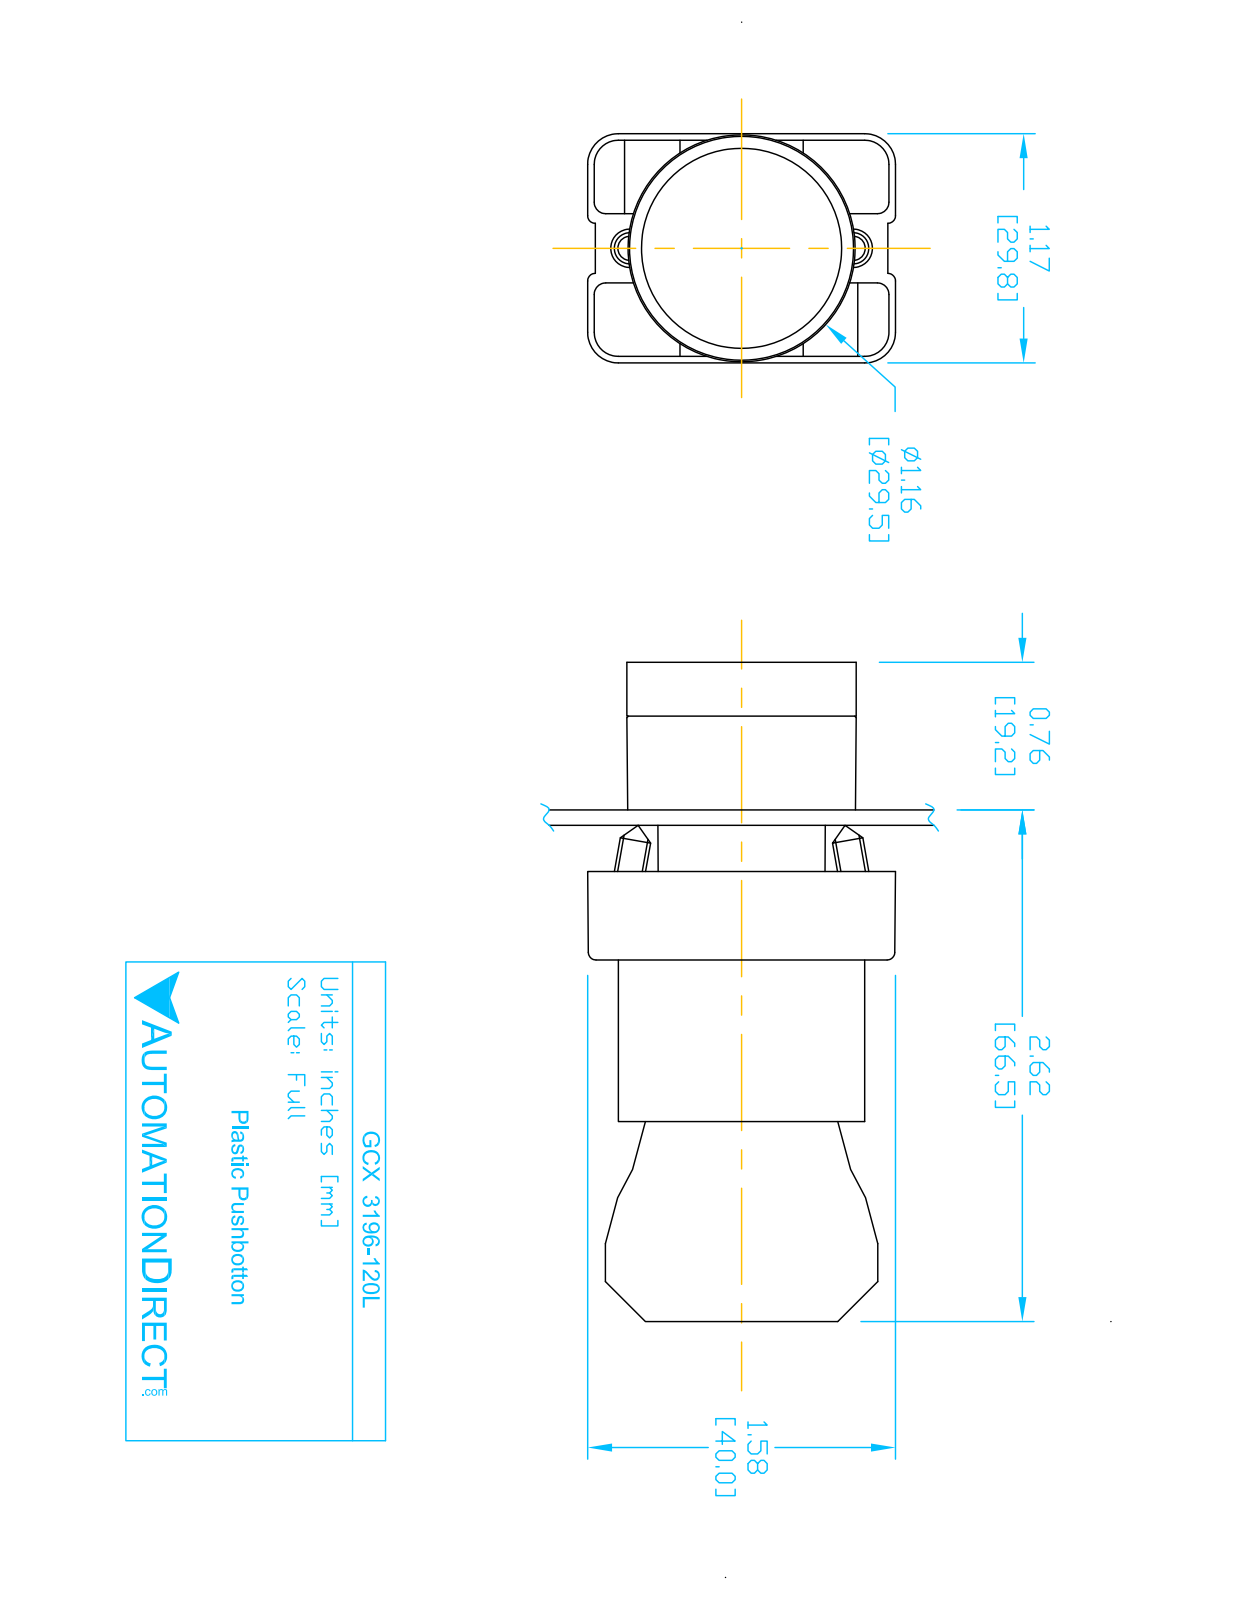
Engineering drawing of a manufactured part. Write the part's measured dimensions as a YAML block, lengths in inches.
part_name: "ECX1050; ECX3029-2; CONTACT BLOCK; GCX3196L OPERATOR (+1 more)"
step_written_by: "SolidWorks 2016 (AUTOMOTIVE_DESIGN)"
units: inches
bodies: {solids: 8, faces: 431, planar: 252, cylindrical: 148, other: 31}
overall_size: [3.319, 1.581, 1.177]
volume: 2.794
surface_area: 38.77
round_holes:
  - {diameter: 0.079, count: 2}
  - {diameter: 0.124, count: 2}
  - {diameter: 0.13, count: 2}
  - {diameter: 0.087, count: 1}
  - {diameter: 0.197, count: 1}
  - {diameter: 0.469, count: 1}
  - {diameter: 0.878, count: 1}
  - {diameter: 0.888, count: 1}
  - {diameter: 1.024, count: 1}
round_bosses_or_shafts:
  - {diameter: 0.157, count: 4}
  - {diameter: 1.175, count: 1}
  - {diameter: 1.004, count: 1}
  - {diameter: 0.945, count: 1}
  - {diameter: 0.856, count: 1}
  - {diameter: 0.78, count: 1}
  - {diameter: 0.504, count: 1}
partial_cylinders:
  - {radius: 0.059, count: 24}
  - {radius: 0.041, count: 12}
  - {radius: 0.124, count: 12}
  - {radius: 0.157, count: 12}
  - {radius: 0.039, count: 8}
  - {radius: 0.128, count: 2}
  - {radius: 0.02, count: 1}
  - {radius: 0.063, count: 1}
face_to_face_distances: [0.827, 0.579, 2.02, 1.193, 1.171, 0.276, 2.295, 1.469, 0.031, 0.033]
hole_center_spacings: [0.236, 0.544, 0.472, 0.49]
